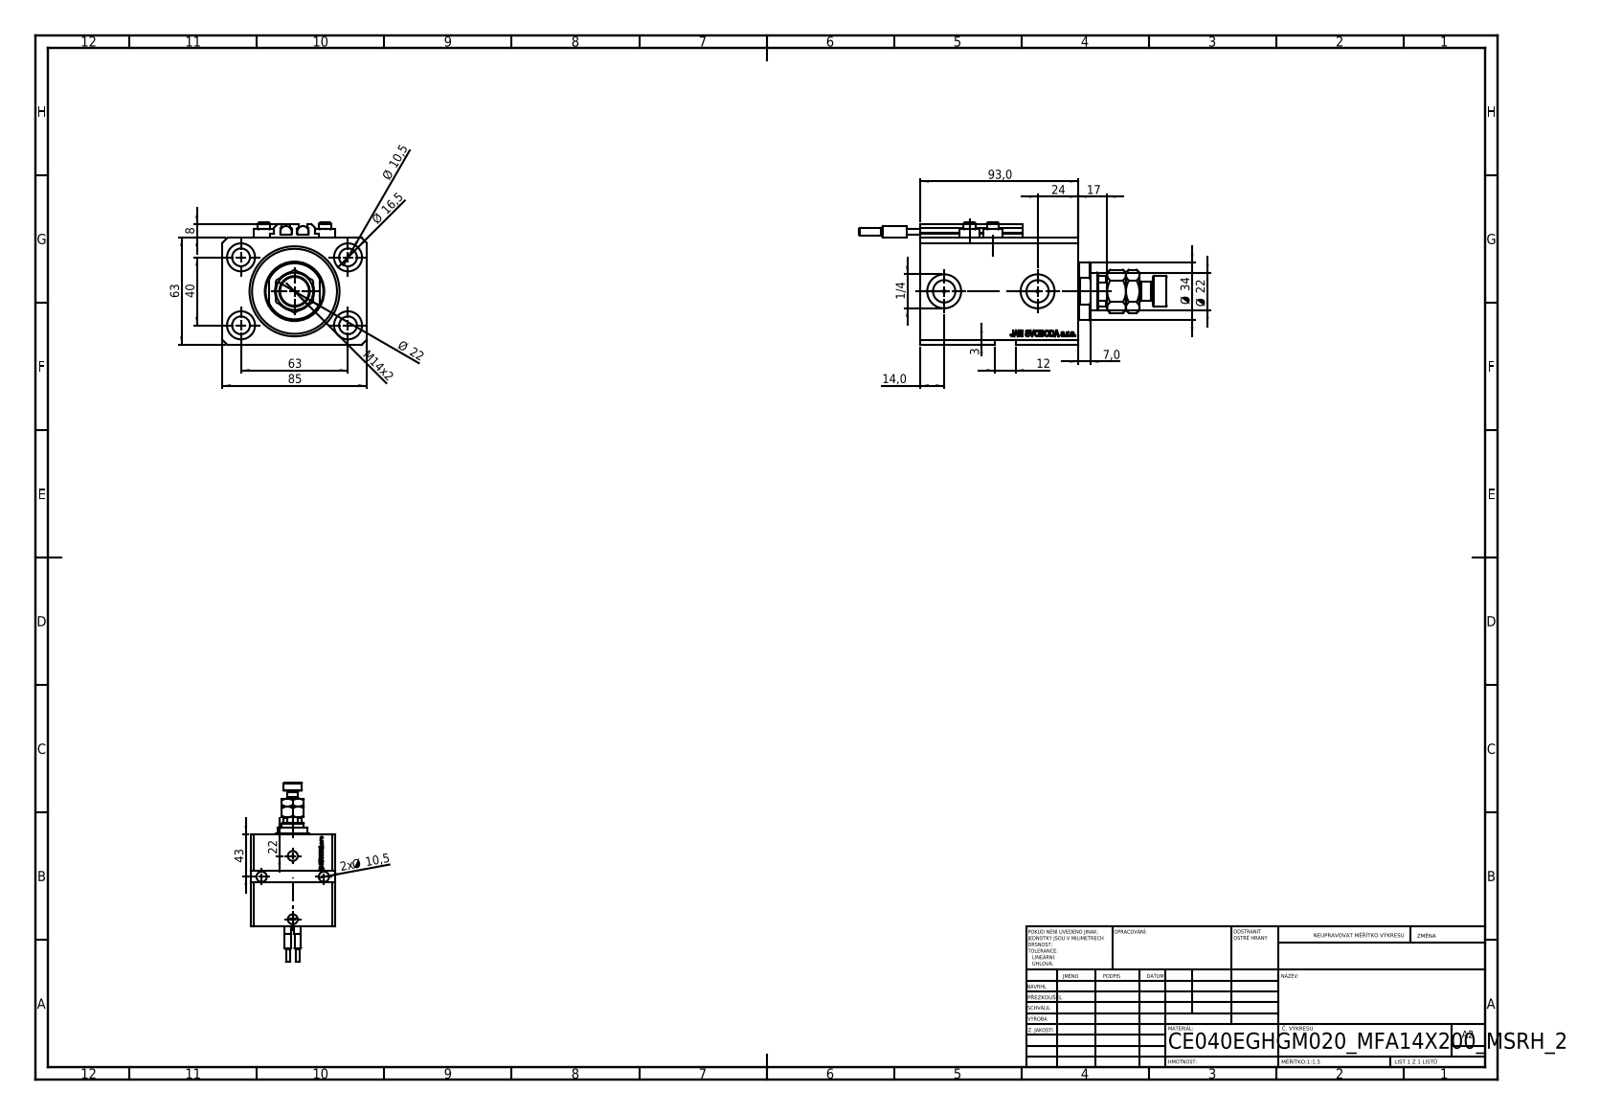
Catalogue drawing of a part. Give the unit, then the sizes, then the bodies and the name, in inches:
Units: inches
Overall size (bounding box): 7.126 × 3.346 × 2.835
Round holes (diameter × count): ⌀0.413 ×6, ⌀0.049 ×4, ⌀0.157 ×4, ⌀0.65 ×4, ⌀0.394 ×2, ⌀0.518 ×2, ⌀0.787 ×2, ⌀0.492 ×1, ⌀0.866 ×1, ⌀1.575 ×1, ⌀2.087 ×1
Round bosses / shafts (diameter × count): ⌀0.457 ×4, ⌀0.276 ×4, ⌀0.268 ×2, ⌀0.256 ×2, ⌀0.157 ×2, ⌀1.339 ×1, ⌀0.709 ×1, ⌀0.433 ×1
Partial cylindrical surfaces — rounded edges, fillets, slot ends (radius × count): R0.008 ×10, R0.413 ×1
Main face-to-face distances: 2.48, 3.346, 3.661, 0.669, 2.992, 0.449, 2.543, 3.213, 0.118, 2.559
Hole centre spacings: 1.469, 2.48, 0.535, 0.606, 0.983, 1.103, 1.119, 1.324
Volume: 27.55 in³ · Surface area: 157.7 in²
Bodies: 11 solids, 1191 faces (583 planar, 142 cylindrical, 466 other)
Part name (STEP PRODUCT): SWITCH_V250CE; V250CE_E_Body; V250CE_VC_E; MFA (+2 more)
STEP written by: SolidWorks 2019 (CONFIG_CONTROL_DESIGN)
